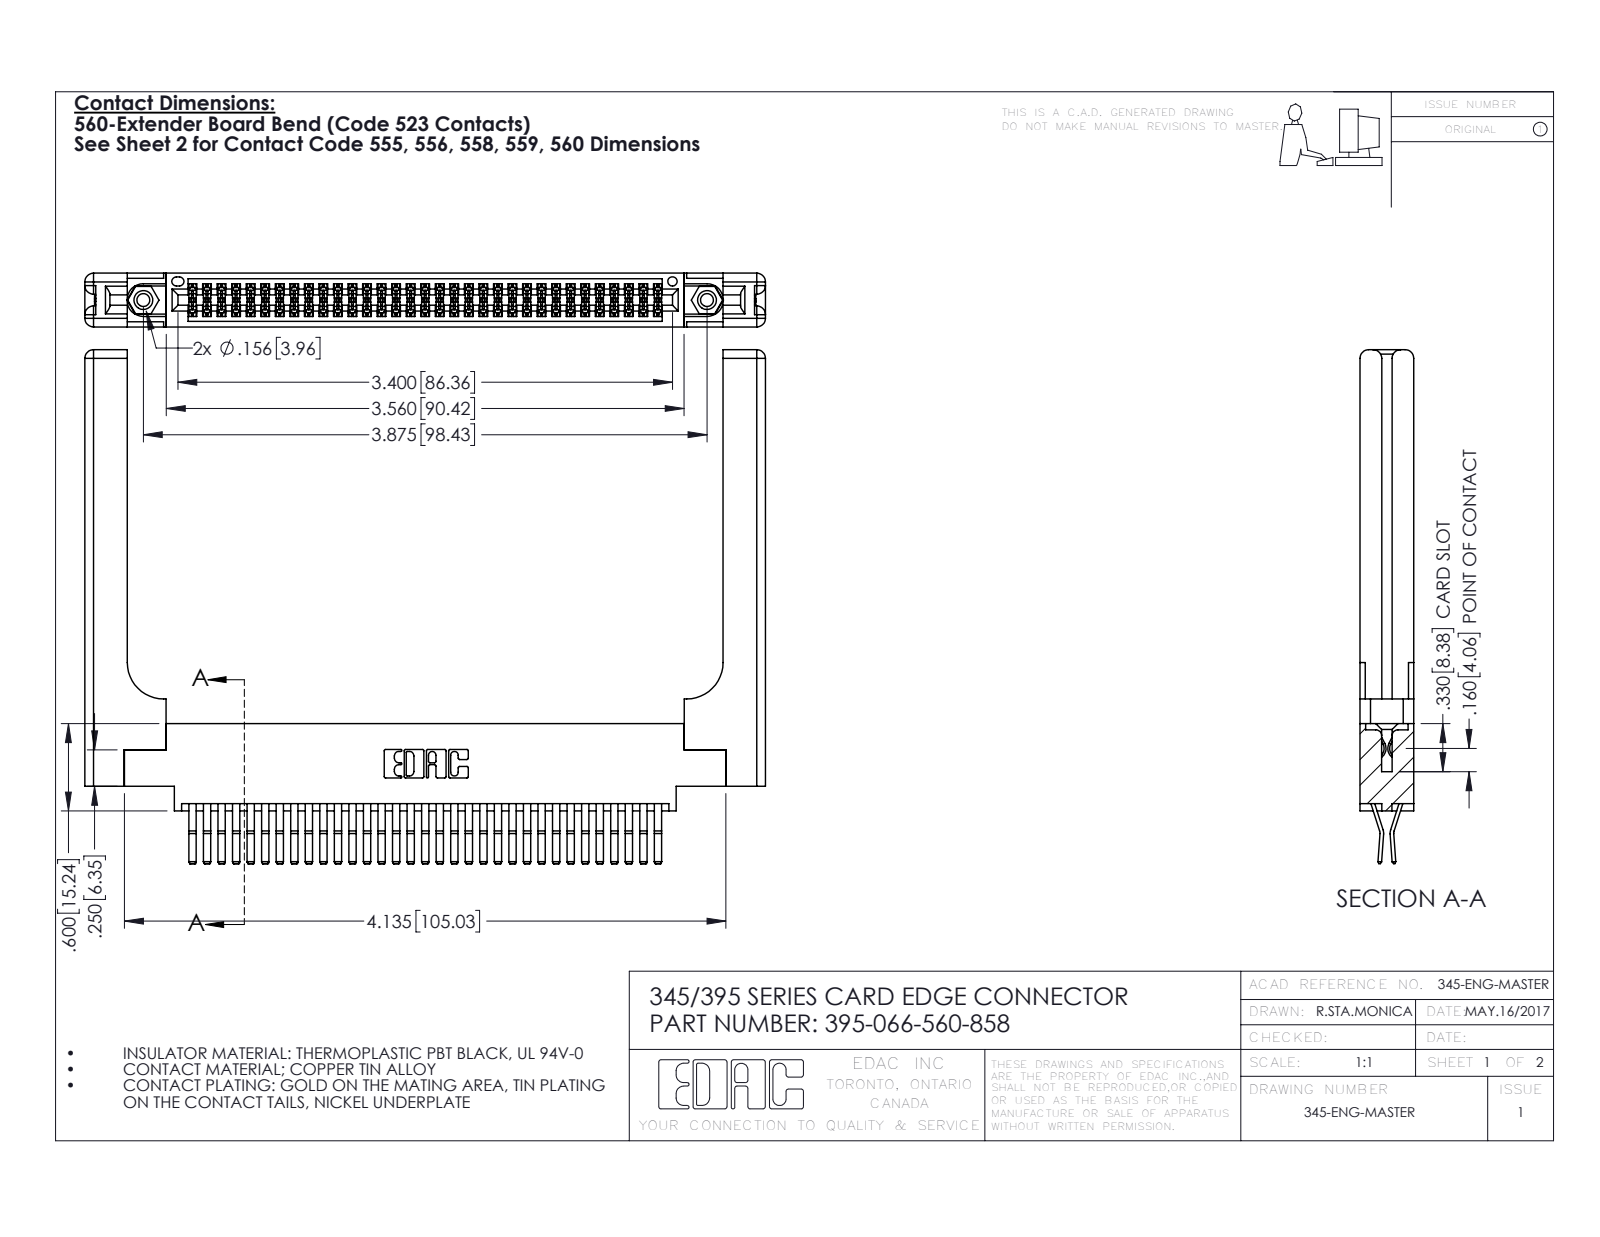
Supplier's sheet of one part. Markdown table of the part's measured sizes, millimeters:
| quantity | value |
| --- | --- |
| part name | 345-250-001_345-250-001-102; 345 Part_0.170 Offset - 0.156 Dia-TH; 345-292-001_560 Tail; 345-220-058_345-220-058 (+1 more) |
| STEP written by | SolidWorks 2016 (CONFIG_CONTROL_DESIGN) |
| units | millimeters |
| bodies | 71 solids, 3818 faces (2410 planar, 1348 cylindrical, 60 other) |
| overall size | 118.8 × 89.7 × 9.4 |
| volume | 20 250 mm³ |
| surface area | 23 550 mm² |
| round holes (diameter × count) | 2.3 × 2, 3.2 × 2, 4 × 2, 1.6 × 1 |
| round bosses / shafts (diameter × count) | 3.9 × 2 |
| partial cylindrical surfaces (radius × count) | 0.2 × 100, 0.3 × 22, 1.5 × 16, 0.2 × 6, 0.8 × 6, 0.7 × 3, 0.3 × 2, 0.4 × 2 |
| main face-to-face distances | 9.4, 1.8, 7.6, 0.6, 2.5, 6.9, 5.1, 5.7, 3.8, 3.8 |
| hole center spacings | 6.9, 92.5, 98.4 |
